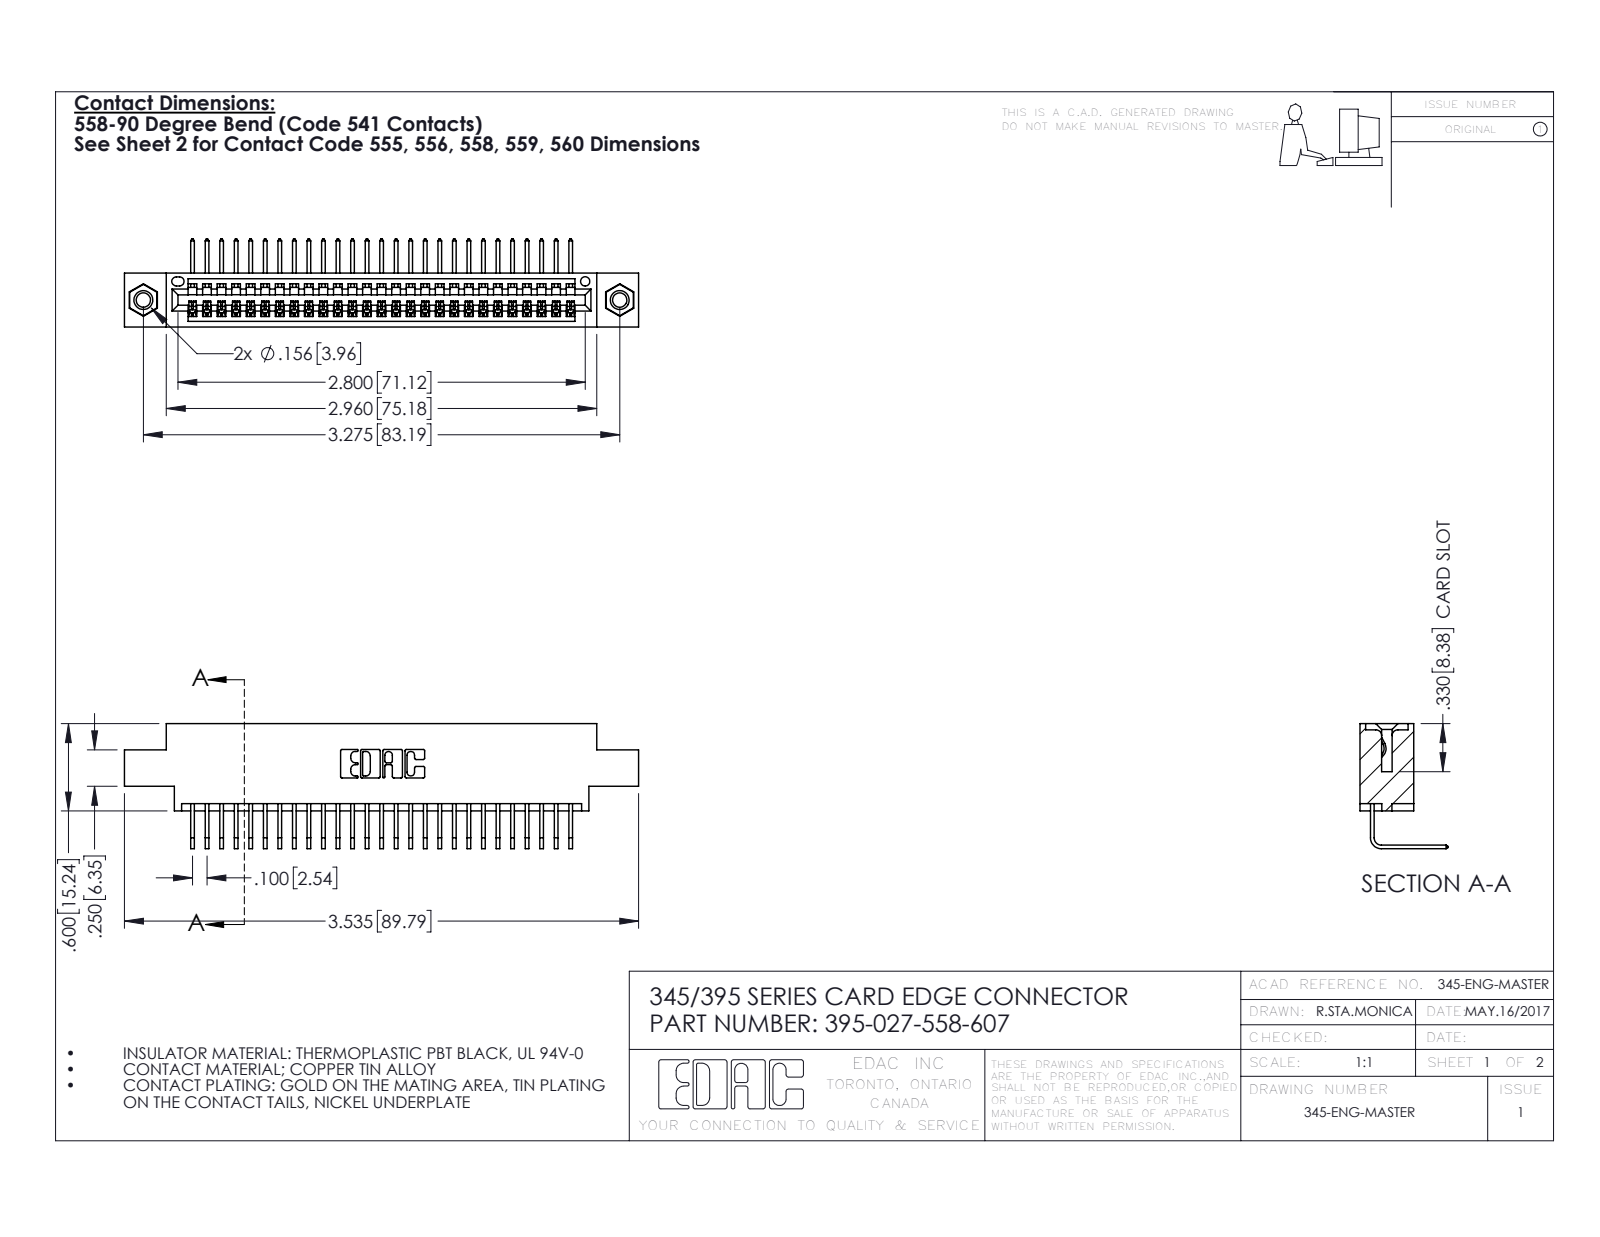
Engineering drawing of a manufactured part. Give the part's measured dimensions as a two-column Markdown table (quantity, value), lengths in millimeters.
| quantity | value |
| --- | --- |
| part name | 345-292-001_558 Tail - 2; 345-250-001_345-250-005-103; 395-027-558-607; 345 Part_0.170 Offset - 0.156 Dia-TI |
| STEP written by | SolidWorks 2016 (CONFIG_CONTROL_DESIGN) |
| units | millimeters |
| bodies | 30 solids, 1810 faces (1250 planar, 544 cylindrical, 16 other) |
| overall size | 89.8 × 21.8 × 15.4 |
| volume | 8 370 mm³ |
| surface area | 11 610 mm² |
| round holes (diameter × count) | 2.5 × 2, 3.2 × 2, 4 × 2, 1.6 × 1 |
| round bosses / shafts (diameter × count) | 3.9 × 2 |
| partial cylindrical surfaces (radius × count) | 0.2 × 54, 0.3 × 22, 0.2 × 6, 0.8 × 6, 0.7 × 3, 0.8 × 2, 1 × 2, 0.4 × 1 |
| main face-to-face distances | 1.8, 7.6, 9.4, 5.1, 2.5, 6.9, 0.6, 5.7, 4.4, 3.8 |
| hole center spacings | 6.9, 77.2, 83.2 |
